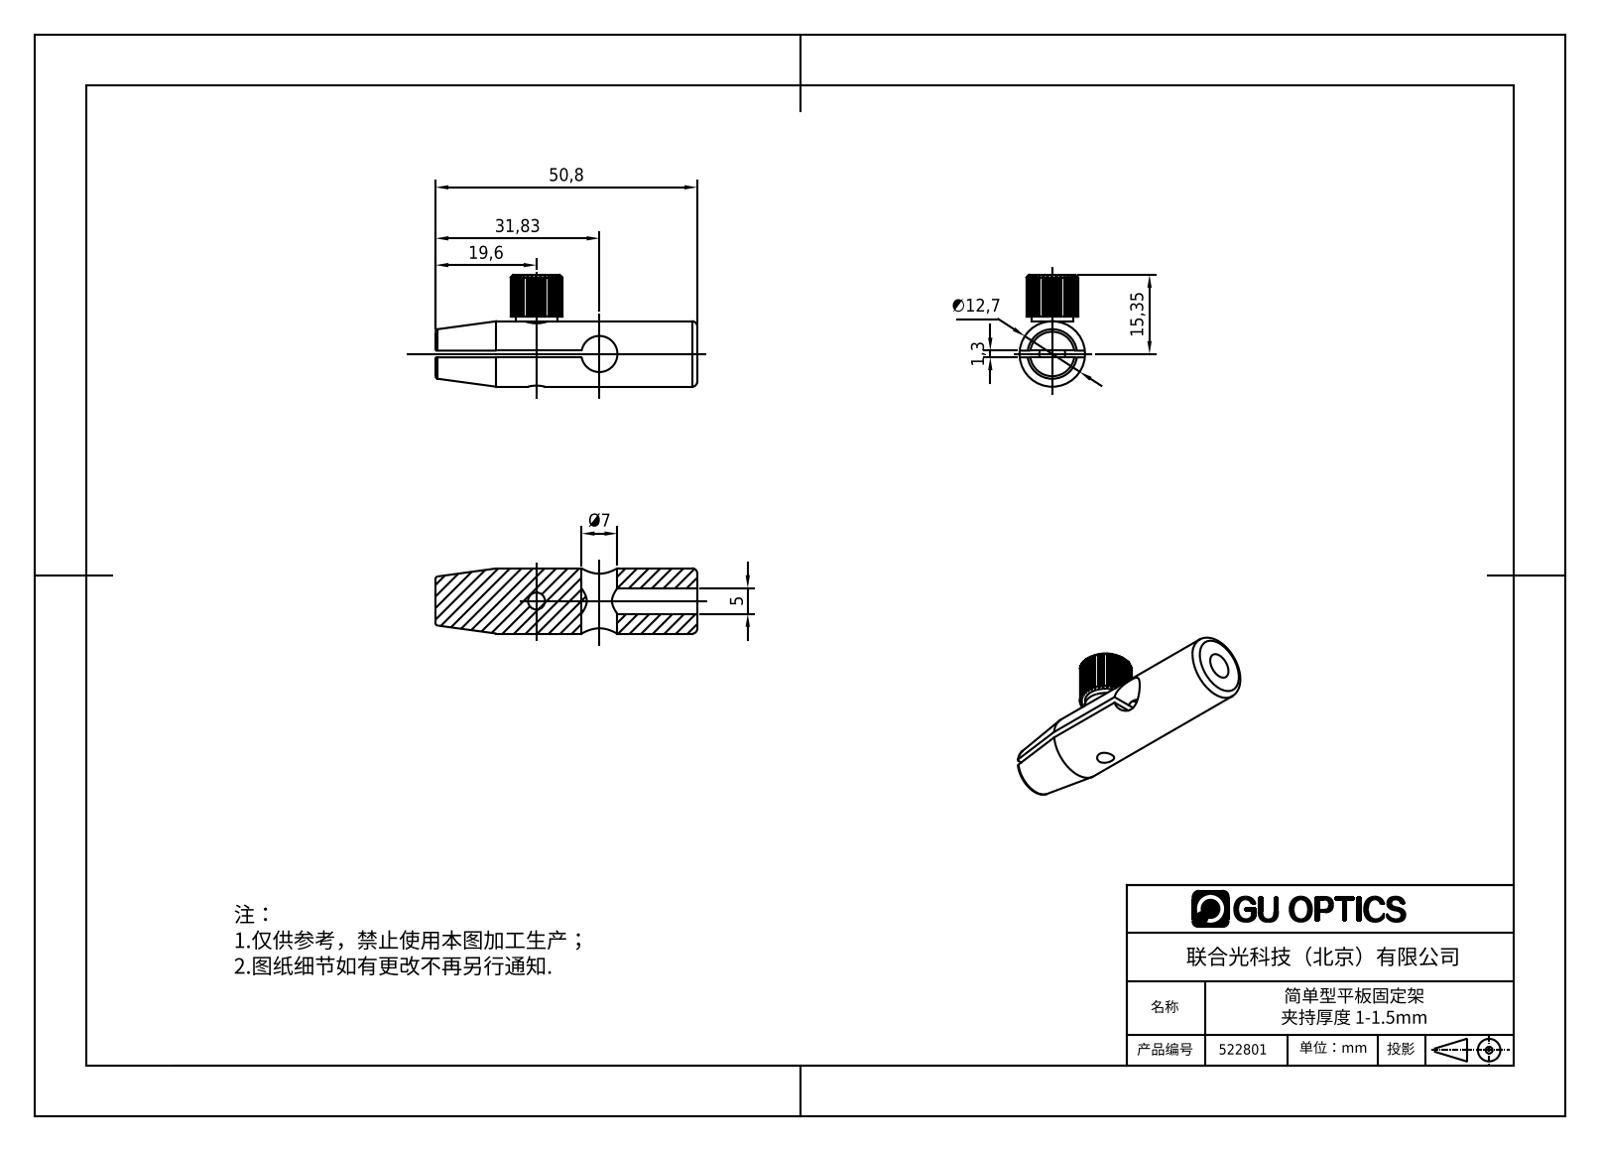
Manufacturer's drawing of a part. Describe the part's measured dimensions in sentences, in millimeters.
The part is named "EPH-1.5". Its 3-D file was written by "SolidWorks 2012 (CONFIG_CONTROL_DESIGN)". It is 0 solids with 132 faces: 83 planar, 43 cylindrical and 6 other. Overall it measures 50.8 by 21.7 by 12.7 millimeters. Round holes: 1 of diameter 3.3, 1 of diameter 5, 1 of diameter 7. Round bosses or shafts: 1 of diameter 12.7, 1 of diameter 8. Partial cylindrical surfaces (rounded edges, fillets, slot ends): 1 of radius 5. The main face-to-face distances are 1.3, 4.65, 16, 14.7, 8, 50.8, 7, 5.7, 9, 6.7.
